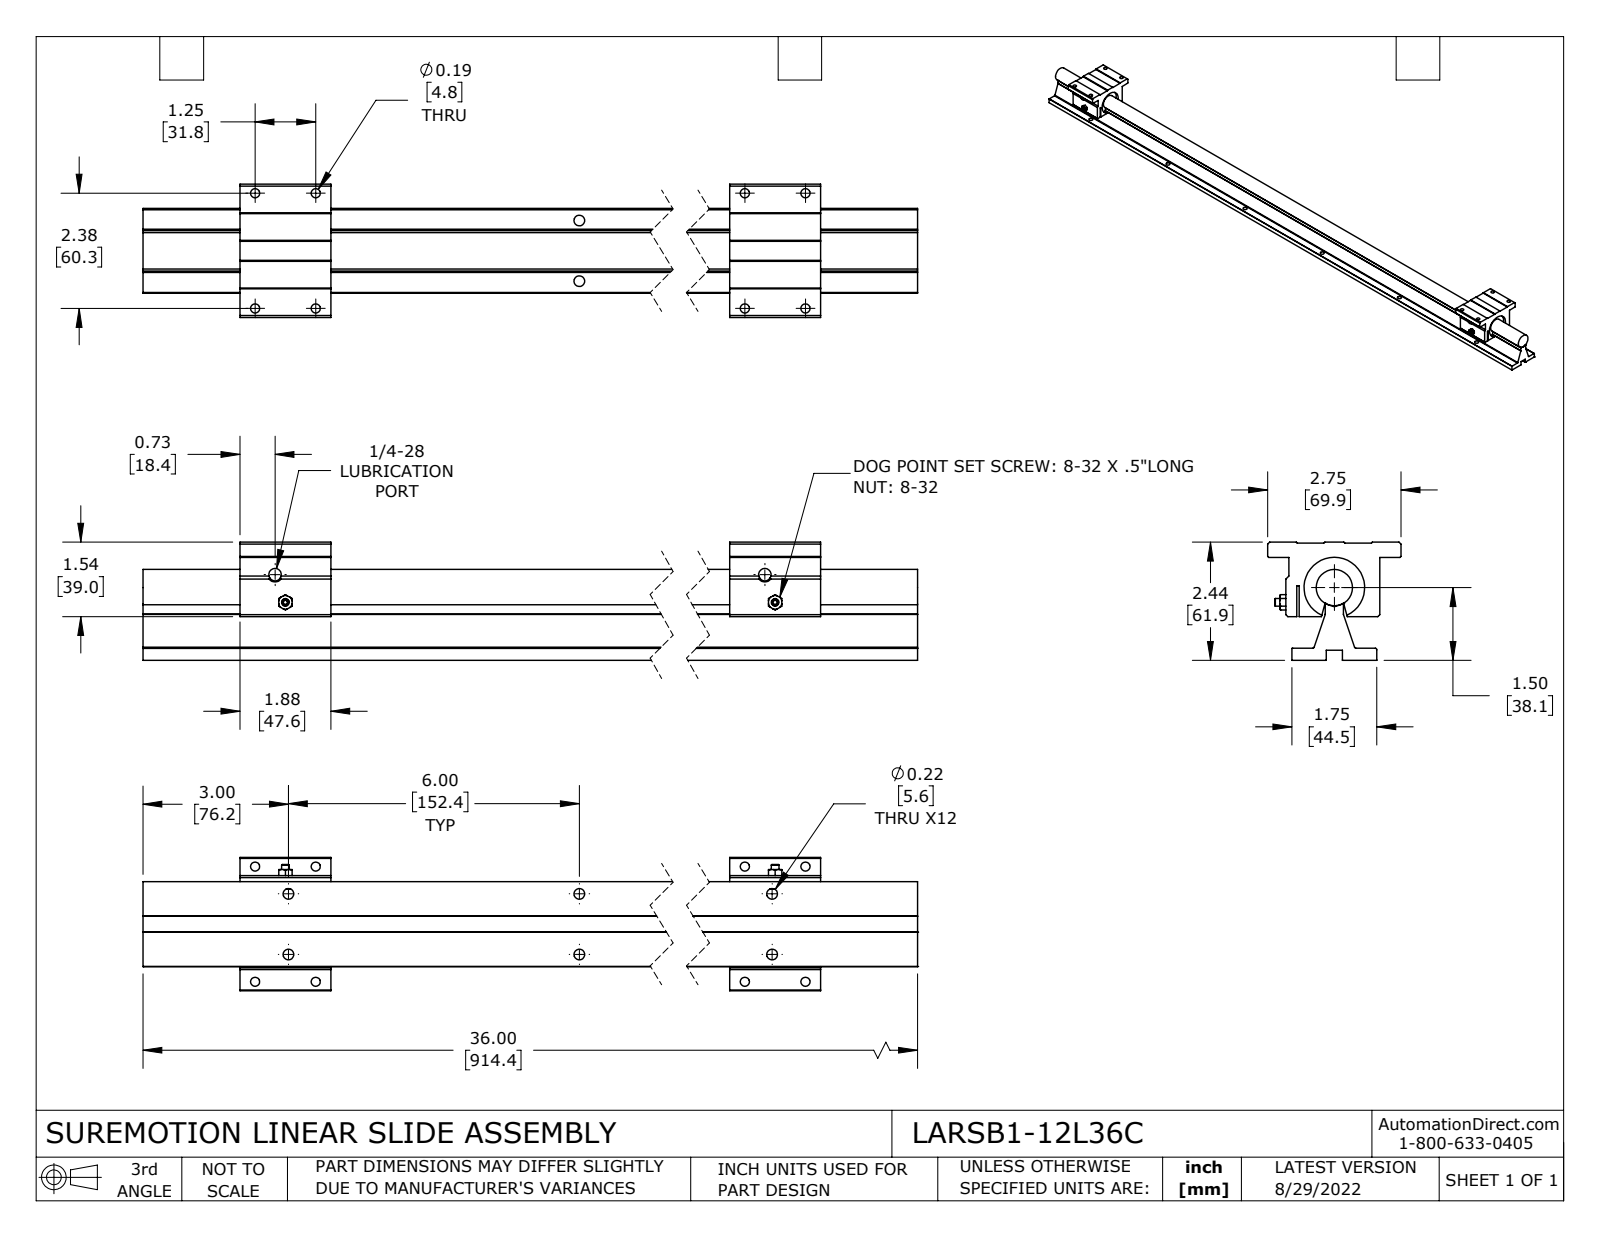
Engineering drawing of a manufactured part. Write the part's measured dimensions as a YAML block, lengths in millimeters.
part_name: "LARSB1-12L36C; LARSB1-12L36C-RAIL; LARSACC-005"
step_written_by: "SolidWorks 2021 (CONFIG_CONTROL_DESIGN)"
units: millimeters
bodies: {solids: 4, faces: 227, planar: 125, cylindrical: 82, other: 20}
overall_size: [914.4, 69.9, 61.9]
volume: 922300
surface_area: 229700
round_holes:
  - {diameter: 5.6, count: 12}
  - {diameter: 4.8, count: 8}
  - {diameter: 6.6, count: 2}
  - {diameter: 19.1, count: 1}
  - {diameter: 31.8, count: 1}
round_bosses_or_shafts:
  - {diameter: 4, count: 2}
partial_cylinders:
  - {radius: 0.8, count: 11}
  - {radius: 1.5, count: 1}
  - {radius: 9.5, count: 1}
face_to_face_distances: [6.4, 18, 26.4, 17.4, 27, 0.6, 8.9, 5.3, 1, 44.5]
hole_center_spacings: [31.8, 152.4, 155.7, 304.8, 306.5, 457.2, 458.3, 765.2]
